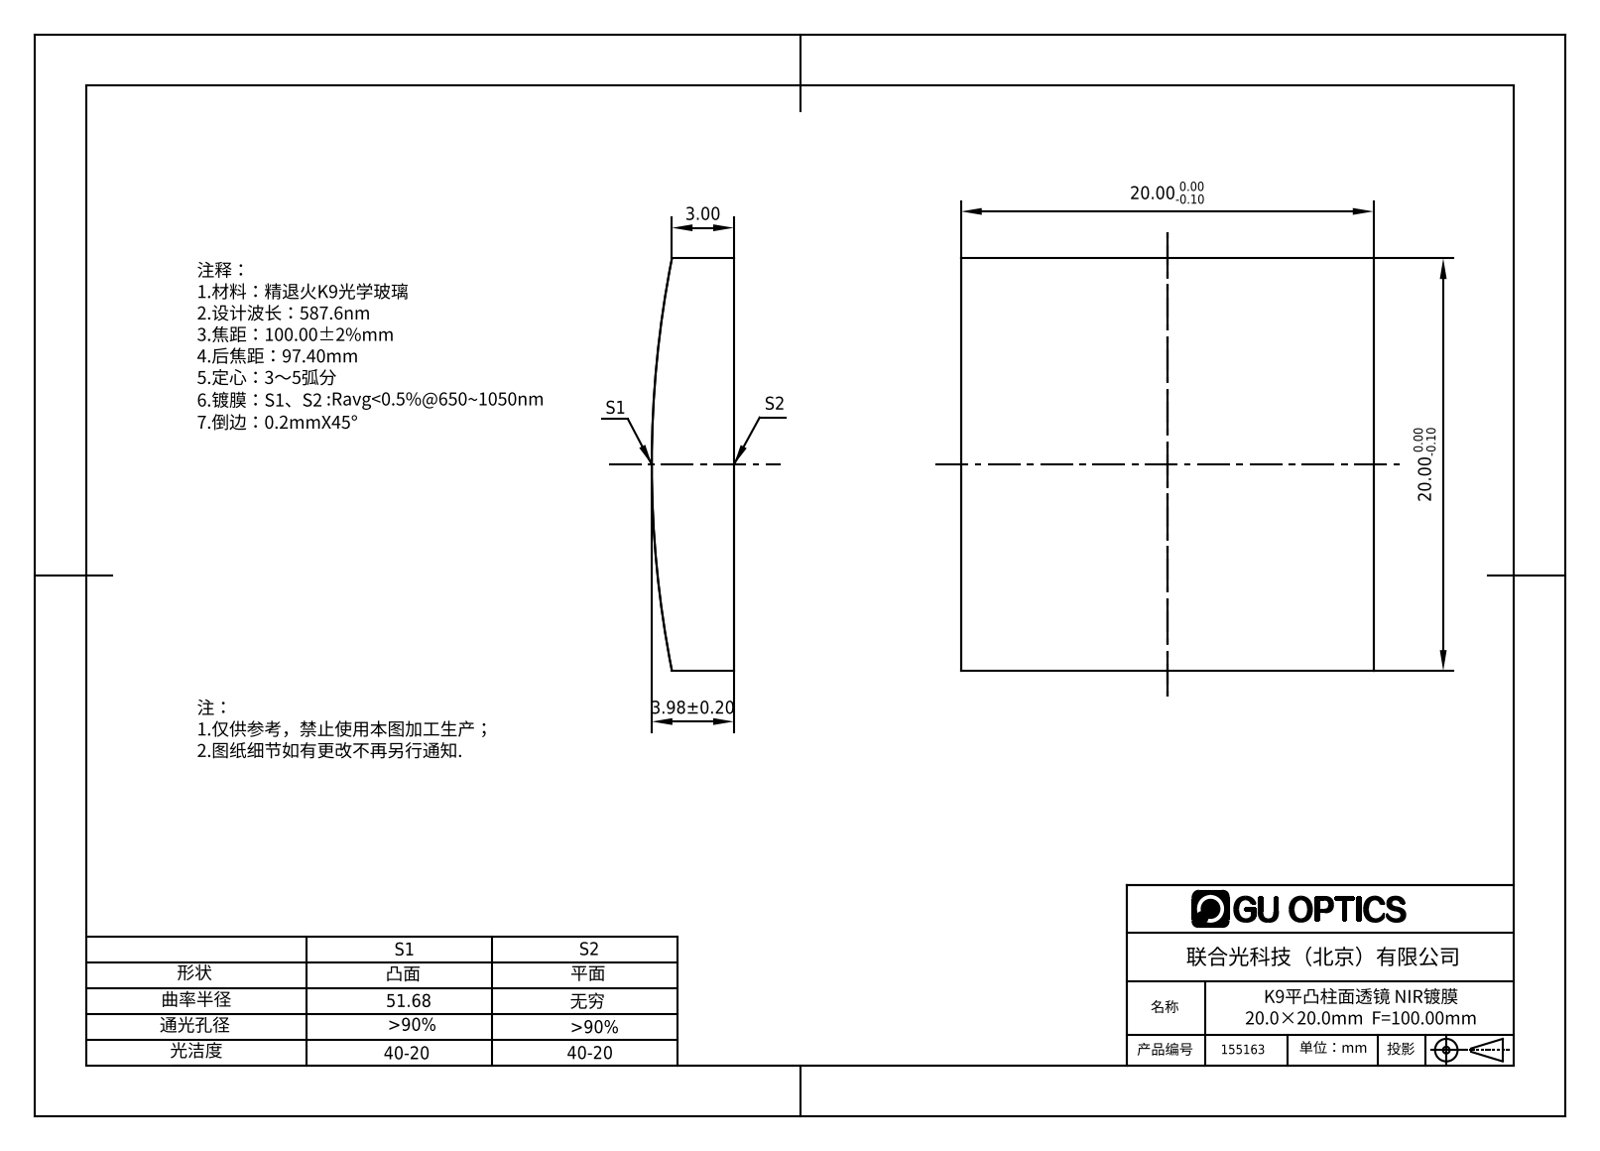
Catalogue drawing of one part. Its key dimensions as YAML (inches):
part_name: "155031"
step_written_by: "SolidWorks 2016 (AUTOMOTIVE_DESIGN)"
units: inches
bodies: {solids: 1, faces: 6, planar: 5, cylindrical: 1, other: 0}
overall_size: [0.787, 0.787, 0.157]
volume: 0.089
surface_area: 1.657
partial_cylinders:
  - {radius: 2.035, count: 1}
face_to_face_distances: [0.787]
